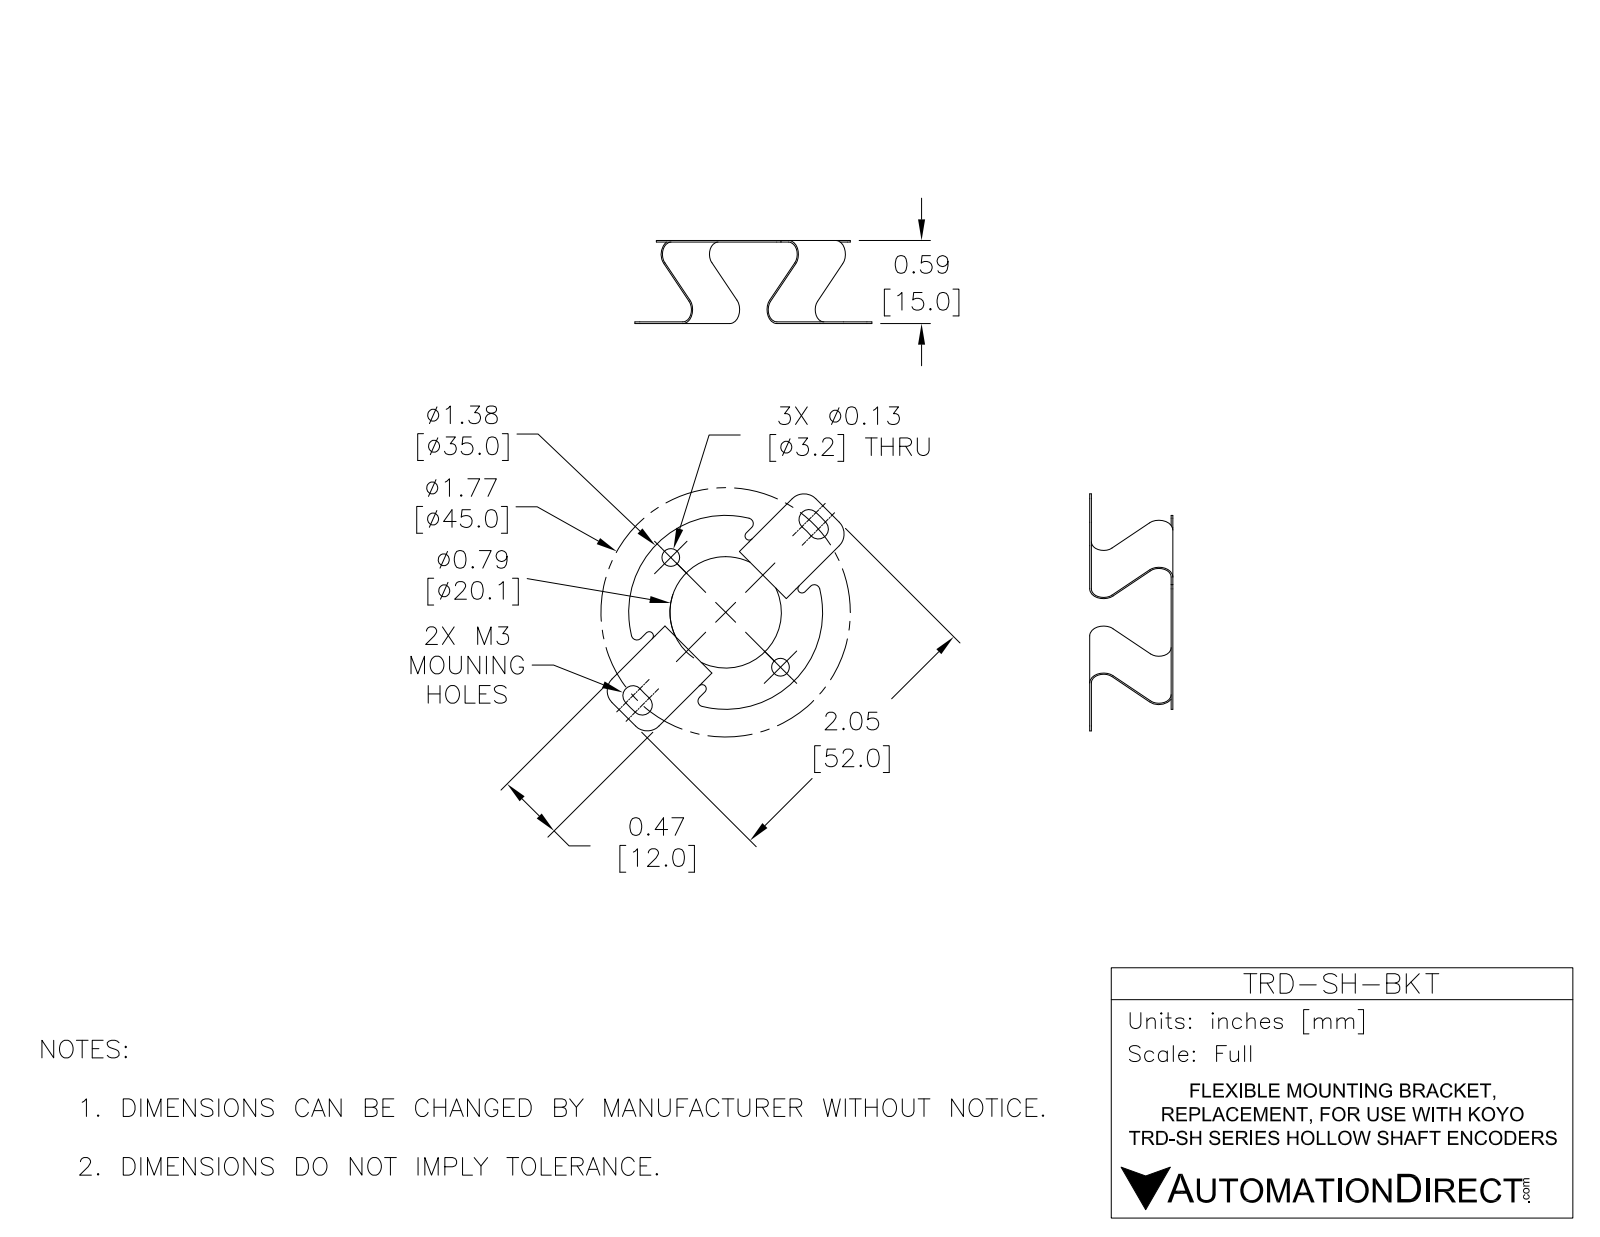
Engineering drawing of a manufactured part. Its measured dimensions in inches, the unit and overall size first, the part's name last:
Units: inches
Overall size (bounding box): 1.684 × 1.684 × 0.591
Round holes (diameter × count): ⌀0.126 ×2, ⌀0.791 ×1
Partial cylindrical surfaces — rounded edges, fillets, slot ends (radius × count): R0.03 ×4, R0.039 ×4, R0.071 ×4, R0.087 ×4, R0.098 ×4, R0.118 ×4, R0.689 ×1, R0.815 ×1
Main face-to-face distances: 0.579, 0.591, 0.567, 0.472, 2.047, 0.059, 0.531
Hole centre spacings: 0.551, 1.102
Volume: 0.024 in³ · Surface area: 4.291 in²
Bodies: 1 solid, 75 faces (32 planar, 43 cylindrical, 0 other)
Part name (STEP PRODUCT): TRD-SH-BKT
STEP written by: SolidWorks 2016 (AUTOMOTIVE_DESIGN)
